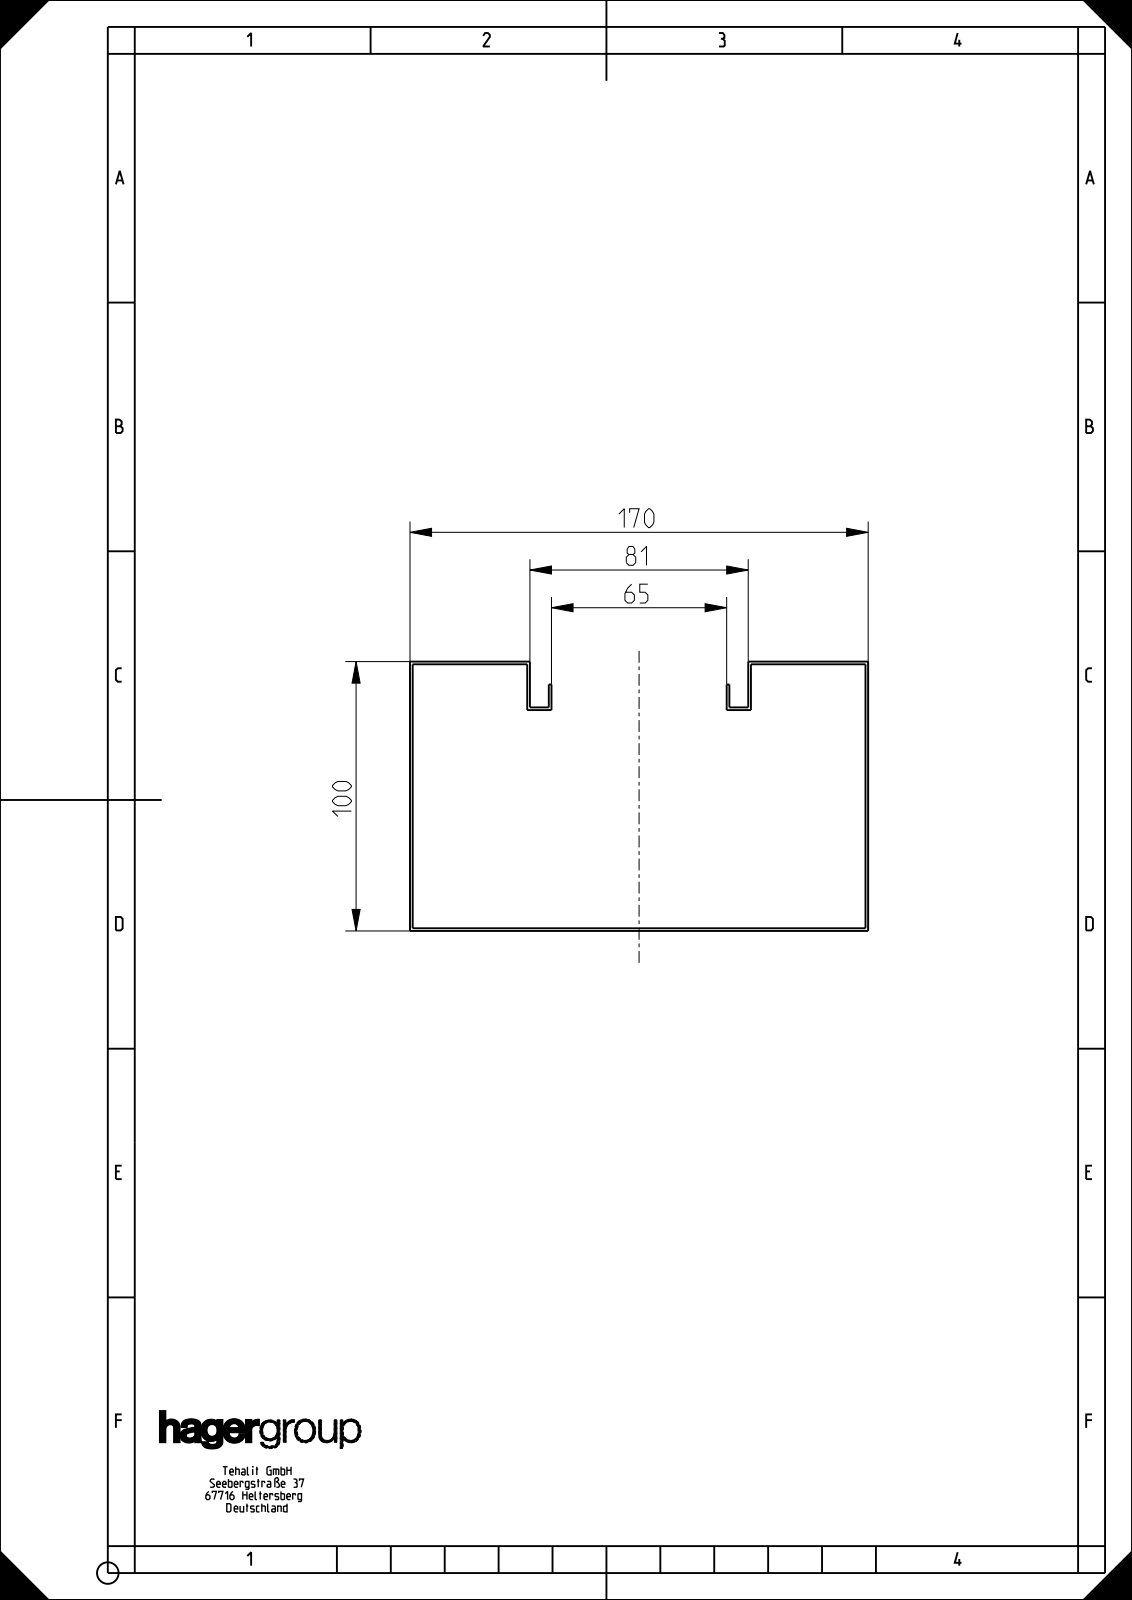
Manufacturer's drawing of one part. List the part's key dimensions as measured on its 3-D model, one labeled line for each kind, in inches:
Part name (STEP PRODUCT): BRS1001701KUN
STEP written by: CREO PARAMETRIC BY PTC INC, 2022162 (AUTOMOTIVE_DESIGN)
Units: inches
Bodies: 1 solid, 1658 faces (1626 planar, 32 cylindrical, 0 other)
Overall size (bounding box): 78.74 × 6.693 × 3.937
Volume: 63.28 in³ · Surface area: 3 230 in²
Round holes (diameter × count): ⌀0.256 ×16
Main face-to-face distances: 0.039, 6.654, 3.898, 6.693, 6.614, 3.937, 3.858, 1.713, 4.941, 3.228
Hole centre spacings: 9.843, 10.221, 19.685, 19.877, 29.528, 29.656, 2.756, 39.37
